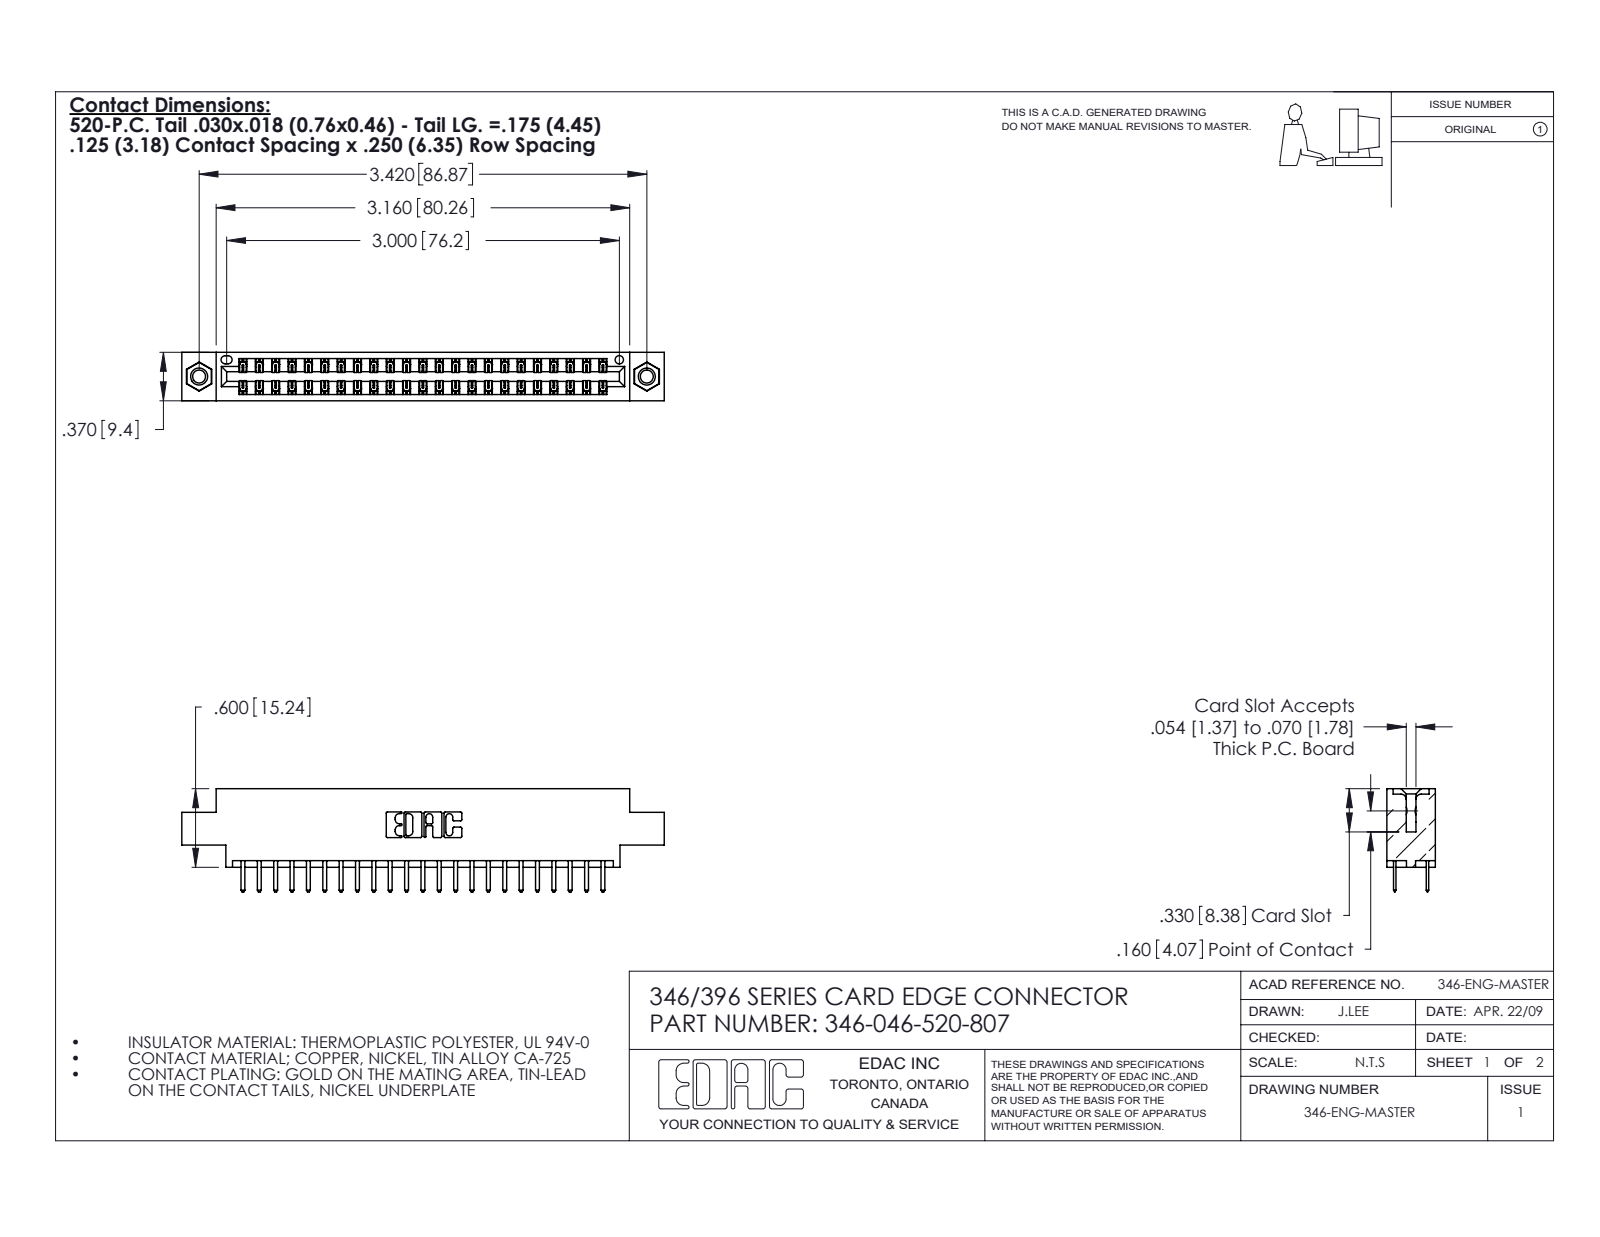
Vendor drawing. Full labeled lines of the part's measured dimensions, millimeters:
Part name (STEP PRODUCT): 346 Part_0.170 Offset - 0.156 Dia-TI; 345-250-001_345-250-005-103; 346-046-520-807; 345-292-001_345-293-120
STEP written by: SolidWorks 2020 (CONFIG_CONTROL_DESIGN)
Units: millimetres
Bodies: 49 solids, 2762 faces (1814 planar, 932 cylindrical, 16 other)
Overall size (bounding box): 93.6 × 20 × 9.4
Volume: 8 780 mm³ · Surface area: 11 950 mm²
Round holes (diameter × count): ⌀2.5 ×2, ⌀3.2 ×2, ⌀4 ×2, ⌀1.6 ×1
Round bosses / shafts (diameter × count): ⌀3.9 ×2
Partial cylindrical surfaces — rounded edges, fillets, slot ends (radius × count): R0.2 ×69, R0.3 ×50, R0.3 ×22, R0.2 ×6, R0.8 ×6, R0.7 ×3, R0.4 ×2, R0.6 ×2
Main face-to-face distances: 1.2, 8.2, 6.4, 9.4, 7, 1.8, 7.6, 0.6, 5.6, 3.8
Hole centre spacings: 6.2, 81.6, 86.9
